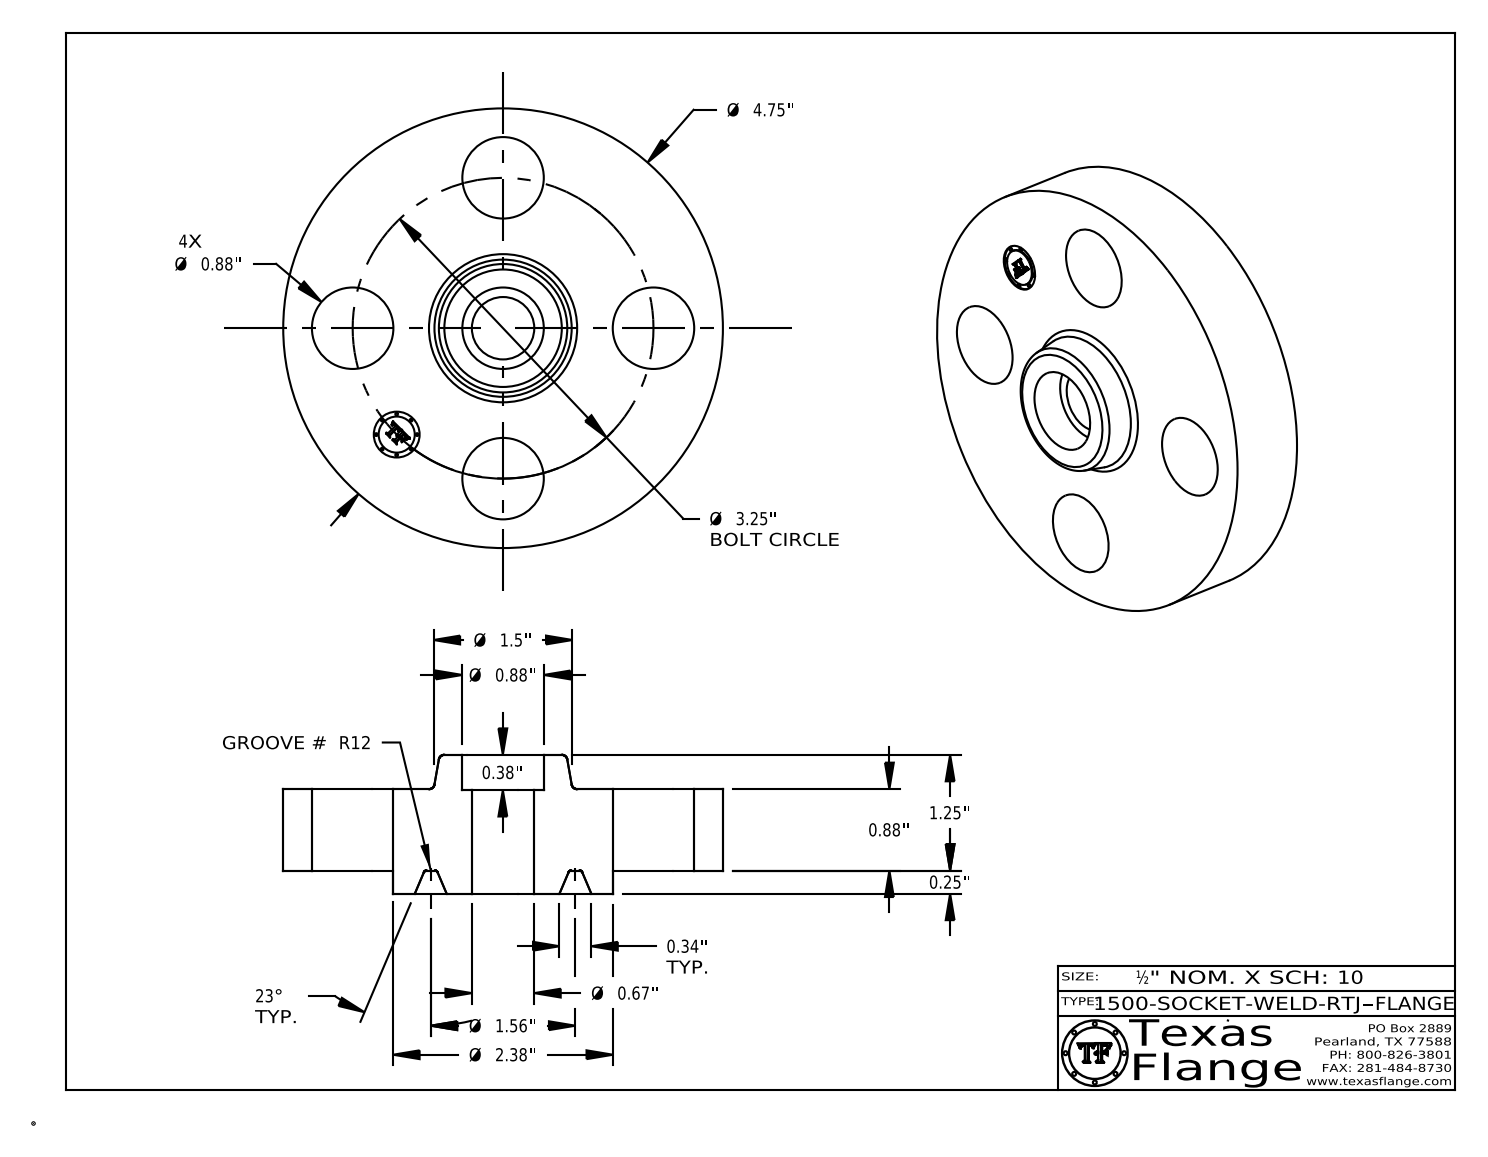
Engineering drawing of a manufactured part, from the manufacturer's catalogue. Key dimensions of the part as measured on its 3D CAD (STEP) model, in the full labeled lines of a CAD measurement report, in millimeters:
Part name (STEP PRODUCT): 1500-SOCKET-WELD-RTJ
STEP written by: CATIA V5 STEP AP214 (AUTOMOTIVE_DESIGN)
Units: millimetres
Bodies: 1 solid, 426 faces (372 planar, 40 cylindrical, 14 other)
Overall size (bounding box): 120.7 × 120.7 × 38.1
Volume: 233 400 mm³ · Surface area: 39 310 mm²
Round holes (diameter × count): ⌀22.4 ×5, ⌀12.6 ×1, ⌀17.1 ×1
Round bosses / shafts (diameter × count): ⌀0.8 ×8, ⌀120.7 ×1, ⌀60.3 ×1, ⌀9.9 ×1
Main face-to-face distances: 22.4, 6.4, 28.7, 38.1, 31.8, 9.4, 28.4, 22.1, 9.7, 28.3
Hole centre spacings: 41.3, 58.4, 31.6, 76.3, 82.6
